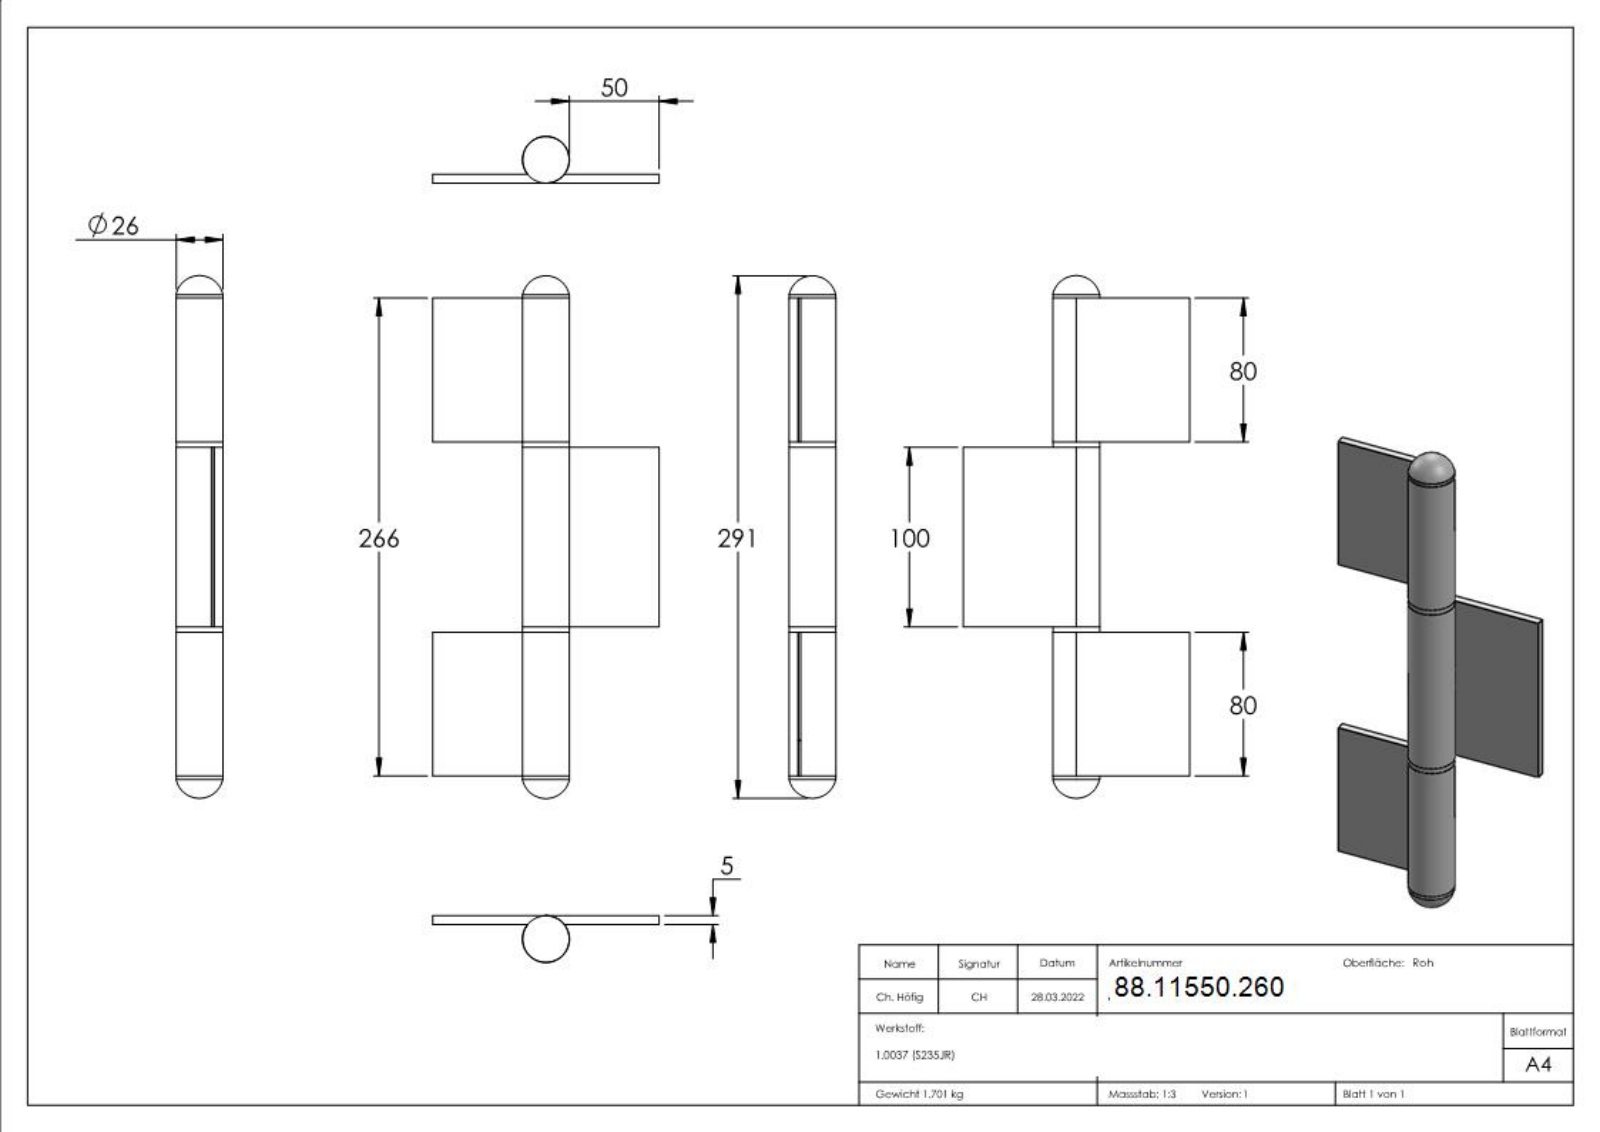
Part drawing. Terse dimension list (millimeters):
name: 550-260; 550-2xx Teil1_550-260 Teil1; 550-2xx Teil4_550-260 Teil4; DIN 125 M4-M20_DIN125 M16 (+2 more)
written by: SolidWorks 2018 (CONFIG_CONTROL_DESIGN)
unit: mm
bodies: 7 solids, 240 faces (126 planar, 14 cylindrical, 100 other)
size: 291 × 126.09 × 26.1
volume: 218 005 mm³; area: 86 202 mm²
holes: 1× ⌀16.1, 1× ⌀17
bosses: 1× ⌀26.1, 1× ⌀26, 1× ⌀16
face distances: 5, 80, 83, 183, 186, 3, 103, 266, 106, 100
